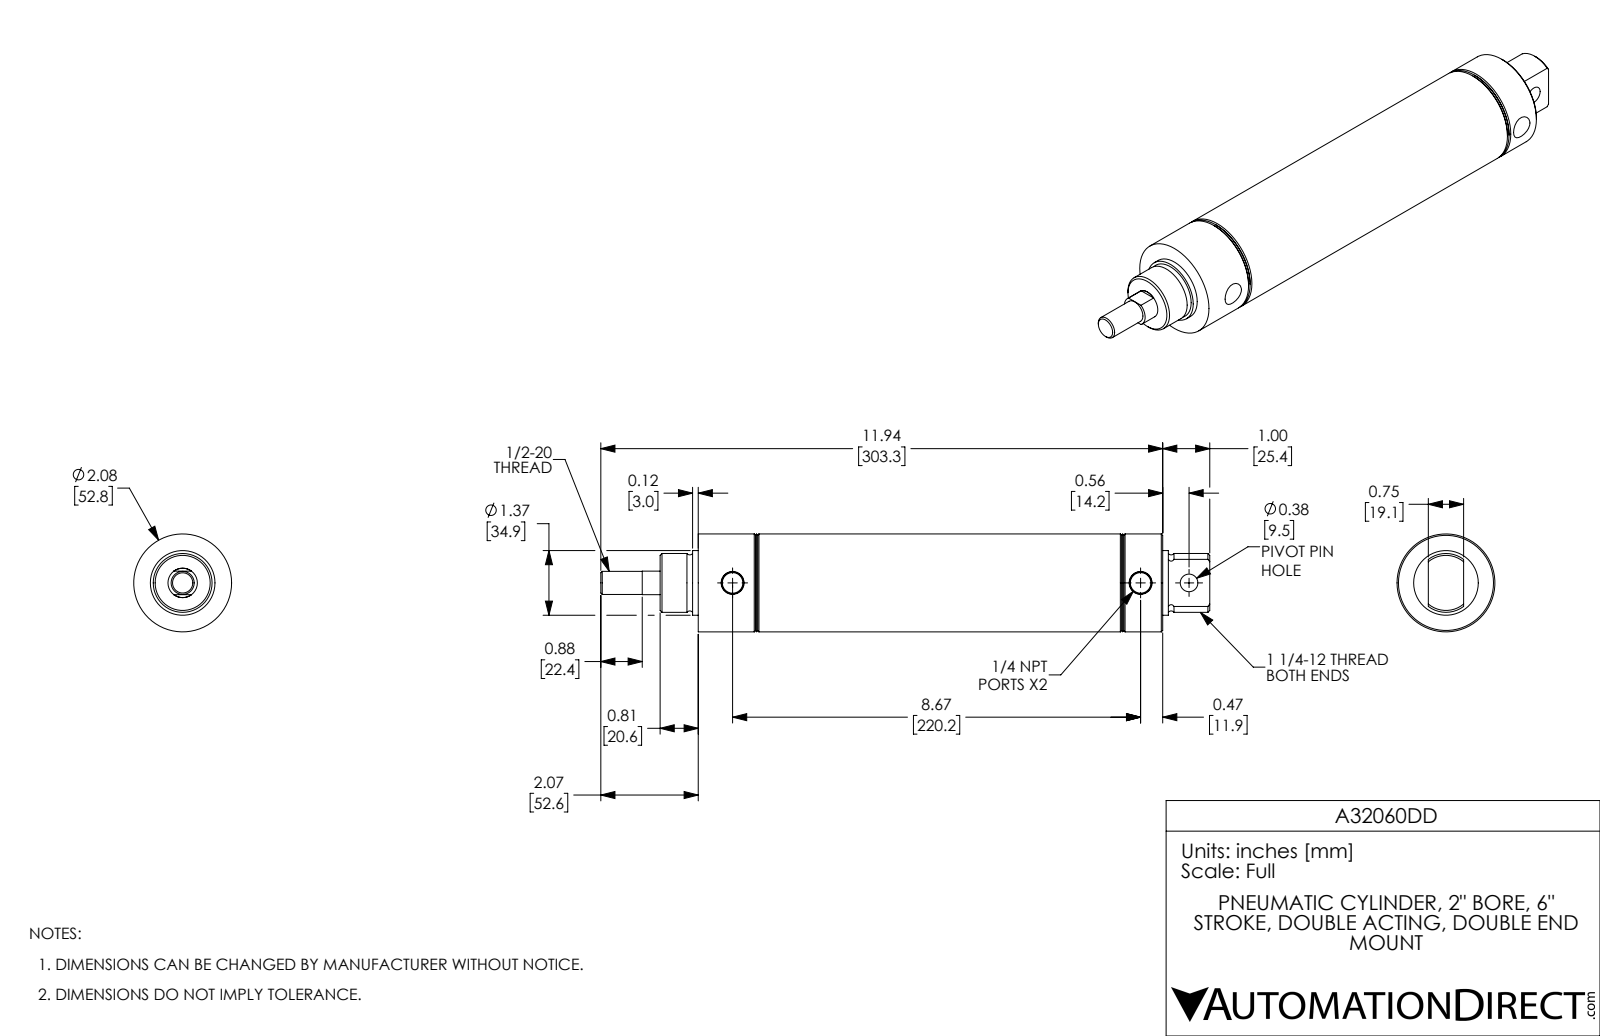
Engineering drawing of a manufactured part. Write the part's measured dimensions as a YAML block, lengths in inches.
part_name: "A32060DD; A32060DD-Rod; A32060DD-MainBody"
step_written_by: "SolidWorks 2017 (AUTOMOTIVE_DESIGN)"
units: inches
bodies: {solids: 2, faces: 88, planar: 20, cylindrical: 30, other: 38}
overall_size: [12.94, 2.08, 2.08]
volume: 18.36
surface_area: 161
round_holes:
  - {diameter: 0.438, count: 2}
  - {diameter: 0.375, count: 1}
  - {diameter: 0.625, count: 1}
  - {diameter: 2, count: 1}
round_bosses_or_shafts:
  - {diameter: 2.08, count: 1}
  - {diameter: 1.373, count: 1}
  - {diameter: 1.25, count: 1}
  - {diameter: 0.491, count: 1}
face_to_face_distances: [1.685, 8.185, 0.5, 6.5, 0.5, 6.5, 6, 8.185, 7.685, 1.685]
hole_center_spacings: [1.03, 8.67, 9.7]
